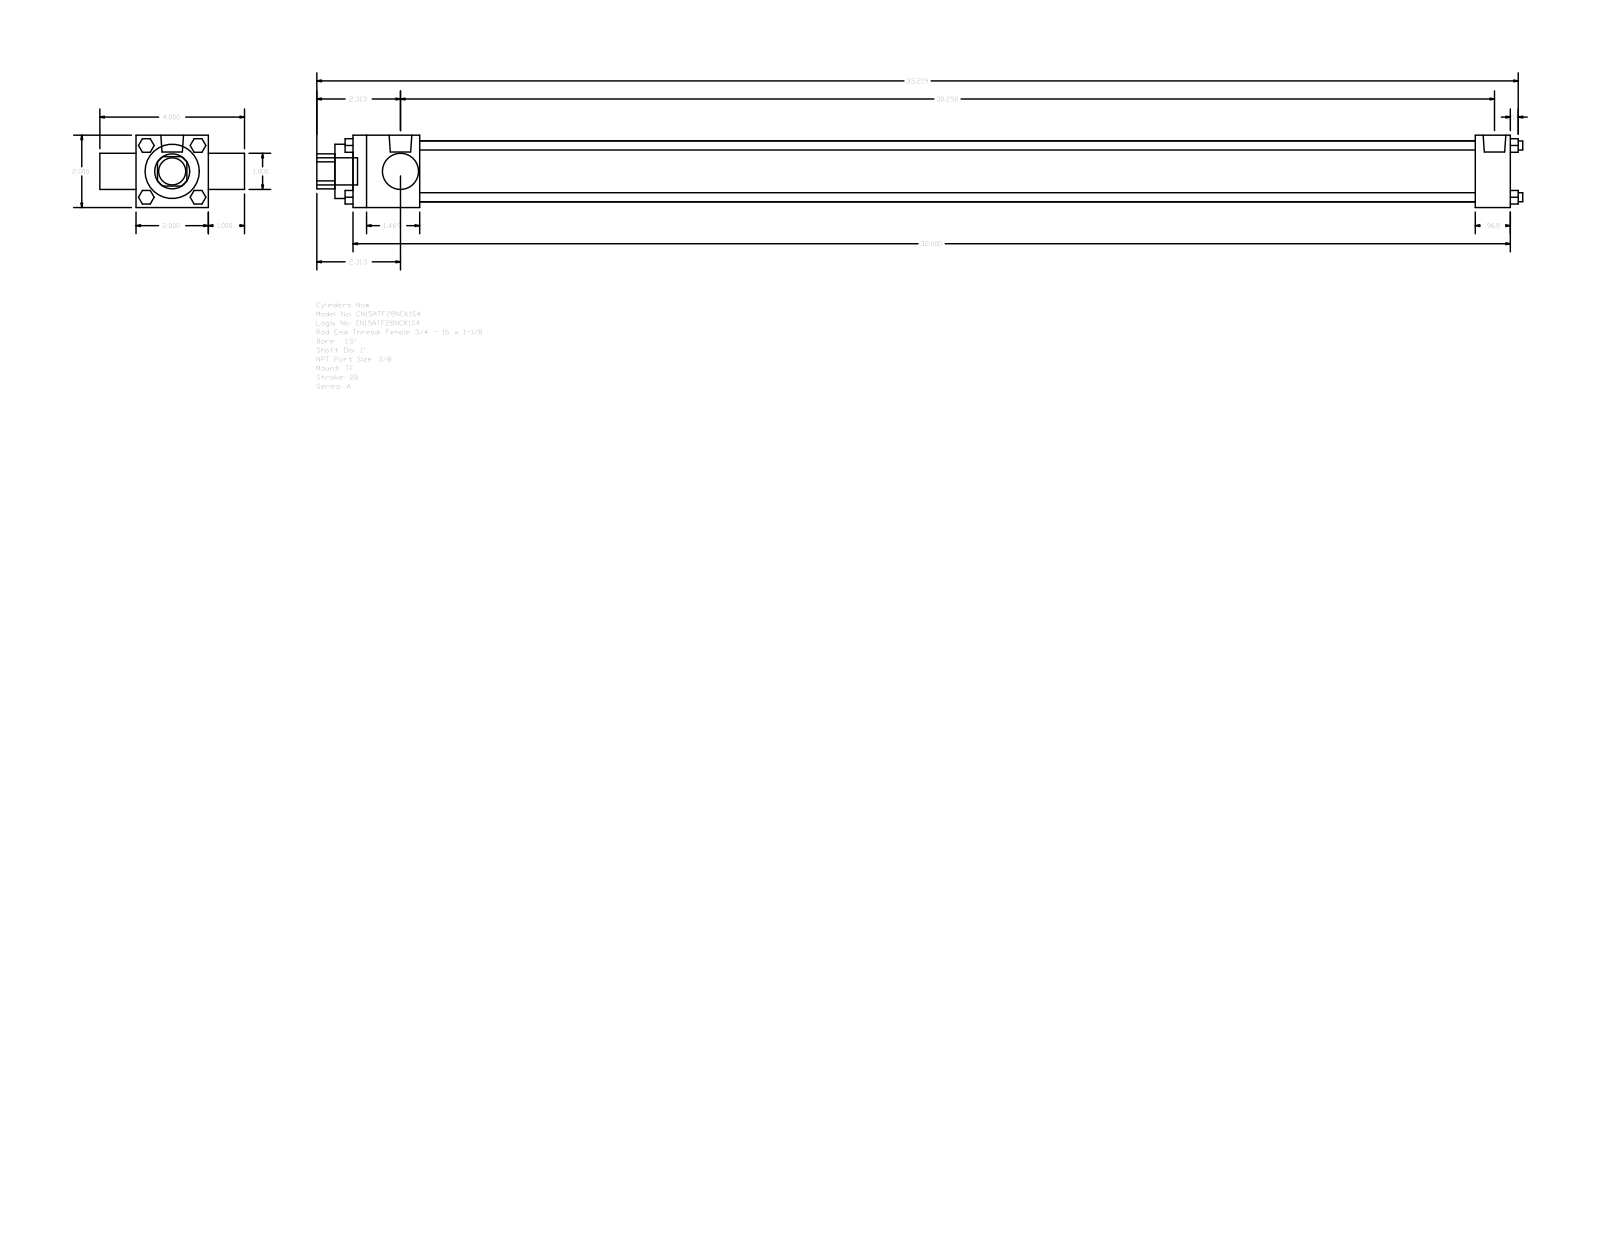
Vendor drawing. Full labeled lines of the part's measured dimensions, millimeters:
Part name (STEP PRODUCT): A_TF__0150_1
STEP written by: GSSL Pune (CONFIG_CONTROL_DESIGN)
Units: millimetres
Bodies: 0 solids, 120 faces (92 planar, 28 cylindrical, 0 other)
Overall size (bounding box): 846.93 × 101.6 × 50.8
Round holes (diameter × count): ⌀25.4 ×2, ⌀38.1 ×1, ⌀42.93 ×1
Round bosses / shafts (diameter × count): ⌀6.35 ×4, ⌀5.56 ×3, ⌀15.93 ×2, ⌀19.05 ×1
Partial cylindrical surfaces — rounded edges, fillets, slot ends (radius × count): R12.29 ×1
Main face-to-face distances: 50.8, 25.4, 812.8, 76.2, 46.83, 788.19, 741.36, 765.97, 24.61, 12.7
